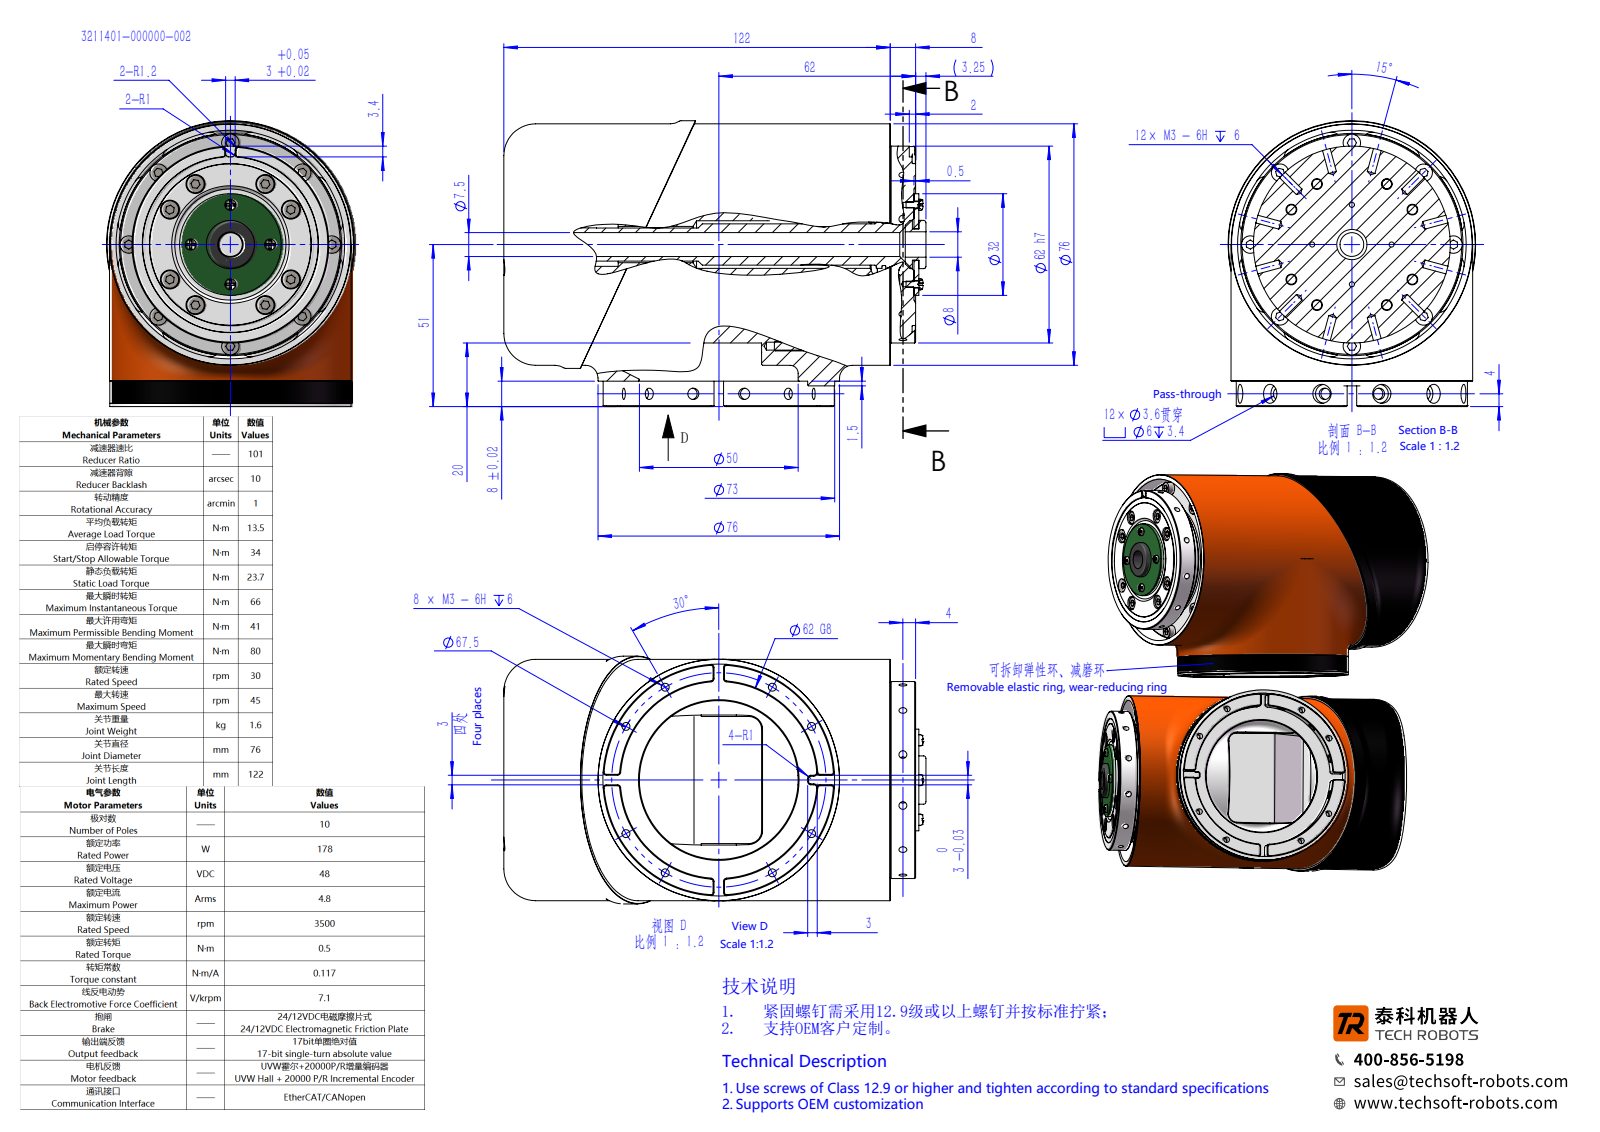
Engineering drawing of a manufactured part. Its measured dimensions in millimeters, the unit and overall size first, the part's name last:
Units: millimetres
Overall size (bounding box): 132.95 × 90 × 78
Round holes (diameter × count): ⌀2.5 ×34, ⌀3.5 ×22, ⌀6 ×20, ⌀3.6 ×12, ⌀3.4 ×8, ⌀1.6 ×4, ⌀2.4 ×4, ⌀2.9 ×3, ⌀5 ×3, ⌀50 ×2, ⌀7.5 ×1, ⌀8 ×1
Round bosses / shafts (diameter × count): ⌀5.5 ×20, ⌀3 ×20, ⌀3.5 ×4, ⌀2 ×4, ⌀78 ×1, ⌀76.1 ×1, ⌀76 ×1, ⌀73 ×1
Partial cylindrical surfaces — rounded edges, fillets, slot ends (radius × count): R1 ×24, R3 ×24, R1.2 ×2, R3.3 ×2, R4 ×2, R1.25 ×1, R28.28 ×1, R33 ×1
Main face-to-face distances: 115.2, 8, 0.5, 129.2, 14, 1.5, 14.5, 129.7, 9, 7.5
Hole centre spacings: 22, 33.75, 11.39, 31.11, 42.5, 25.3, 32, 34.35
Volume: 588 670 mm³ · Surface area: 79 756 mm²
Bodies: 19 solids, 1298 faces (432 planar, 482 cylindrical, 384 other)
STEP written by: SolidWorks 2016 (CONFIG_CONTROL_DESIGN)
